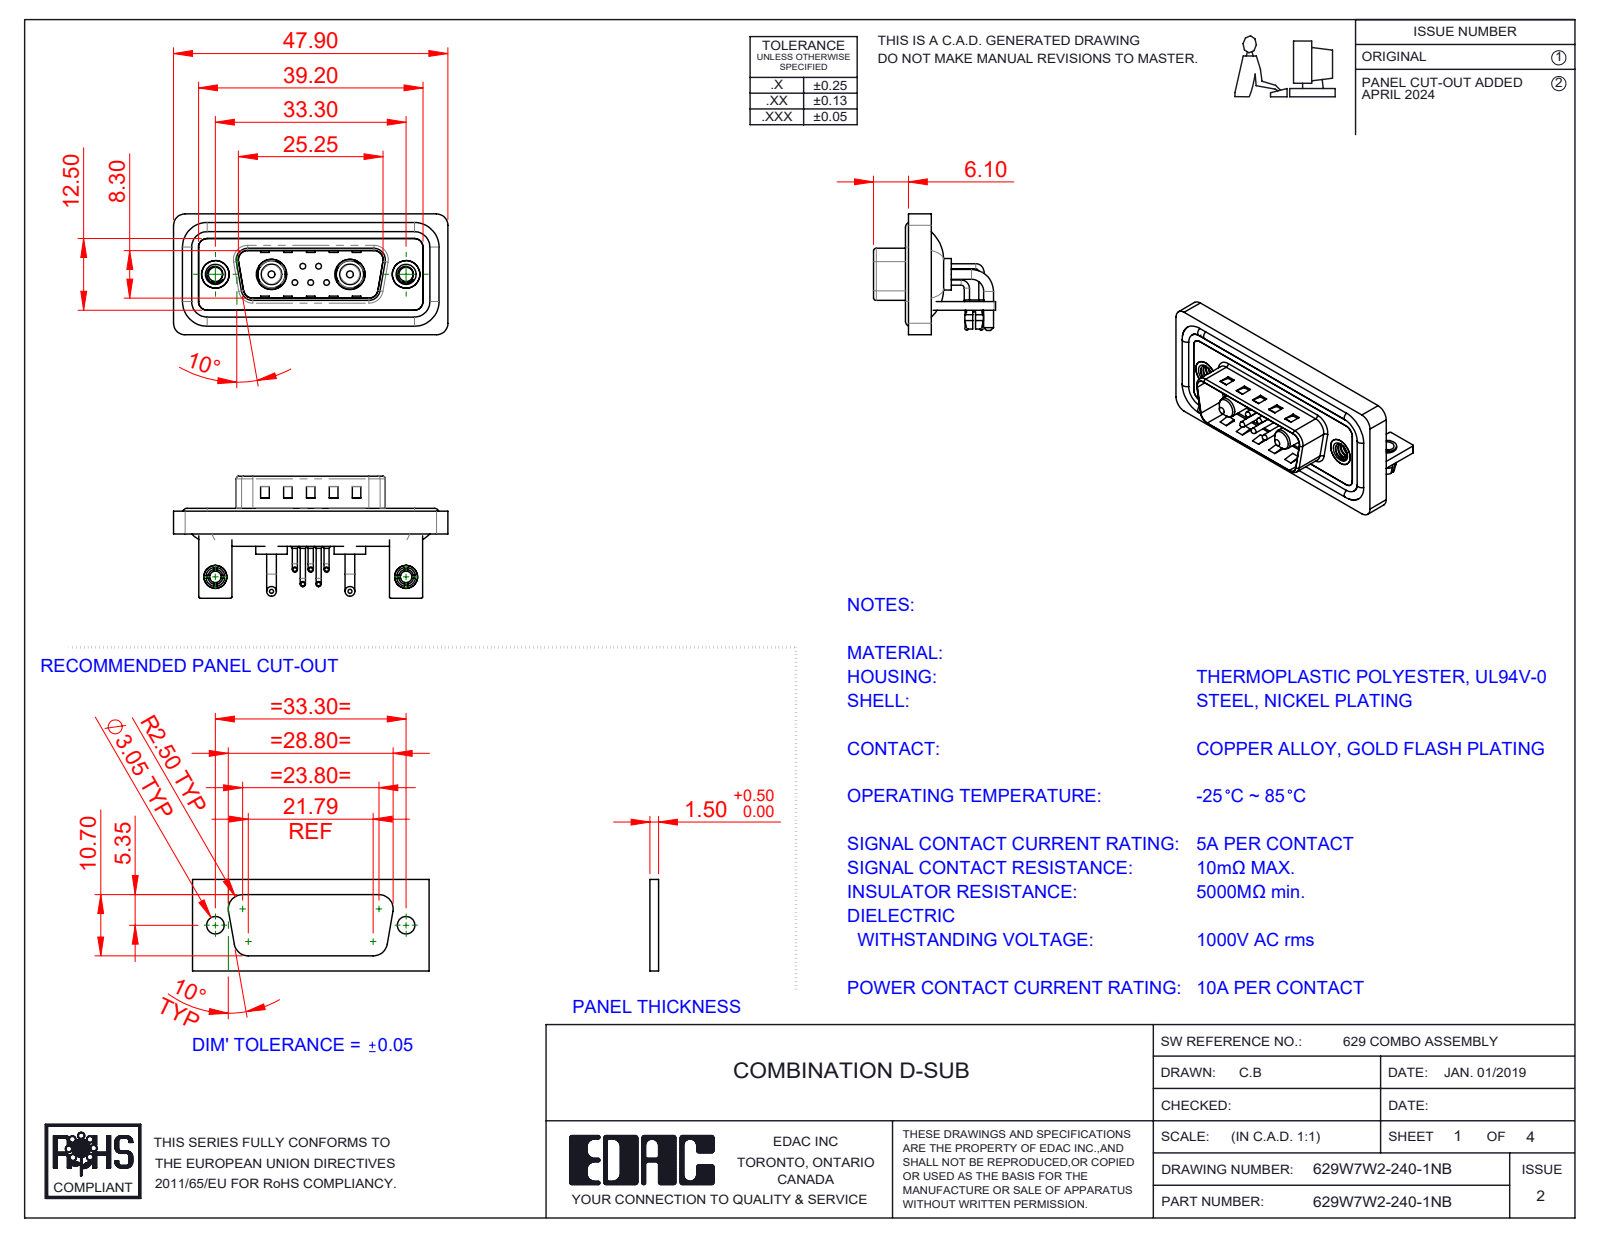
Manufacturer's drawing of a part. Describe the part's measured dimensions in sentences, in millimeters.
The part is named "629Combo Contact Row 1; 629Combo Stabilizer Bracket; 629Combo Shell Rear_15 Contacts; 629W7W2-140-1NB (+7 more)". Its 3-D file was written by "SolidWorks 2023 (CONFIG_CONTROL_DESIGN)". It is 20 solids with 1213 faces: 585 planar, 456 cylindrical and 172 other. Overall it measures 47.9 by 21.3 by 21.1 millimeters. Its volume is 5 873 cubic millimeters and its surface area 9 837 square millimeters. Round holes: 7 of diameter 2, 5 of diameter 0.75, 5 of diameter 1.6, 4 of diameter 2.5, 2 of diameter 3.2, 2 of diameter 4, 2 of diameter 4.8, 2 of diameter 4.85, 2 of diameter 5, 2 of diameter 5.3. Round bosses or shafts: 10 of diameter 0.9, 5 of diameter 1.5, 5 of diameter 1, 5 of diameter 0.65, 4 of diameter 1.7, 4 of diameter 1.6, 2 of diameter 5.5, 2 of diameter 5.2. Partial cylindrical surfaces (rounded edges, fillets, slot ends): 21 of radius 2, 18 of radius 1.5, 16 of radius 0.25, 9 of radius 0.5, 8 of radius 1.6, 5 of radius 1.01, 4 of radius 0.6, 4 of radius 0.65. The main face-to-face distances are 0.4, 1.5, 0.8, 2.9, 2.1, 1.1, 1.6, 1.2, 3.7, 4.5. The hole center spacings are 3.16, 2.77, 9.8, 23.5, 33.3, 4.31, 4.33, 5.03.
